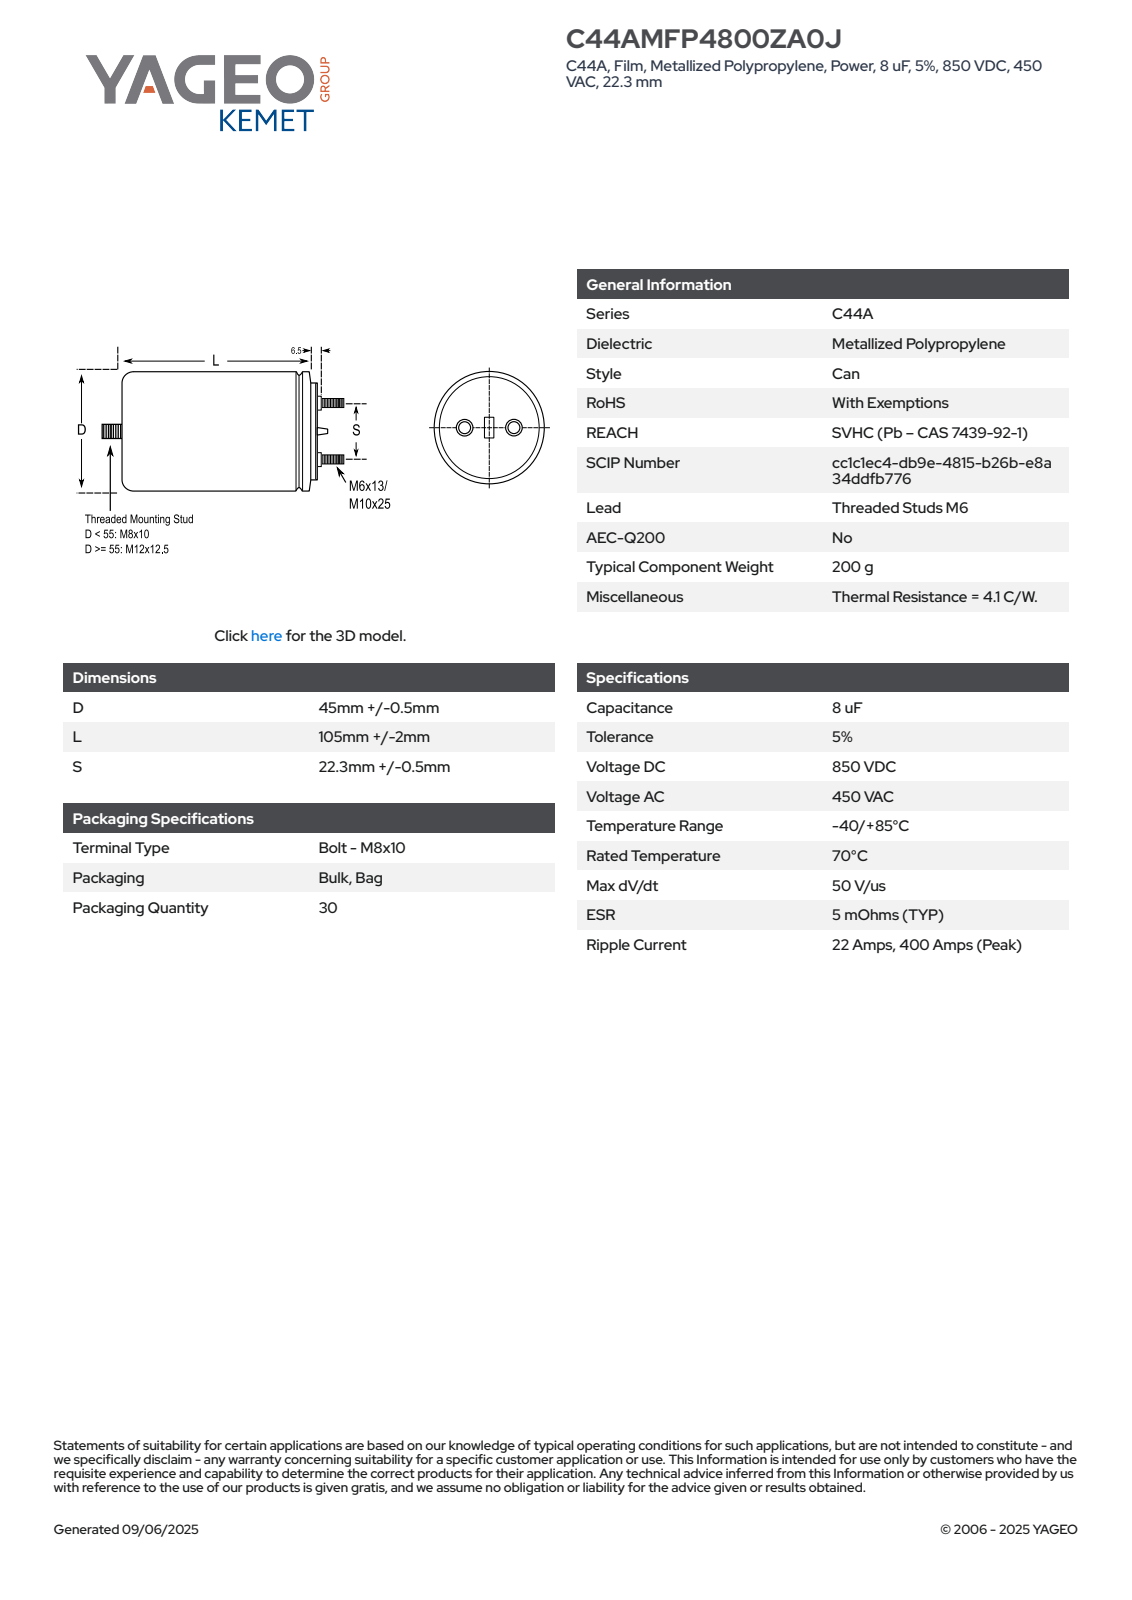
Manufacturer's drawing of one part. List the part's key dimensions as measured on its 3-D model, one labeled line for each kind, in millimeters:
Part name (STEP PRODUCT): CFP_C44A_45X105_D45.5L107S22.3
STEP written by: SolidWorks 2014 (AUTOMOTIVE_DESIGN)
Units: millimetres
Bodies: 1 solid, 102 faces (29 planar, 34 cylindrical, 39 other)
Overall size (bounding box): 136.5 × 45.5 × 45.5
Volume: 178 947 mm³ · Surface area: 19 670 mm²
Round bosses / shafts (diameter × count): ⌀9 ×2, ⌀6 ×2, ⌀45.5 ×1, ⌀35.69 ×1, ⌀8 ×1
Partial cylindrical surfaces — rounded edges, fillets, slot ends (radius × count): R22.74 ×1
Main face-to-face distances: 112, 113.5, 1.5, 126.5, 14.5, 13, 10, 122, 123.5, 136.5
